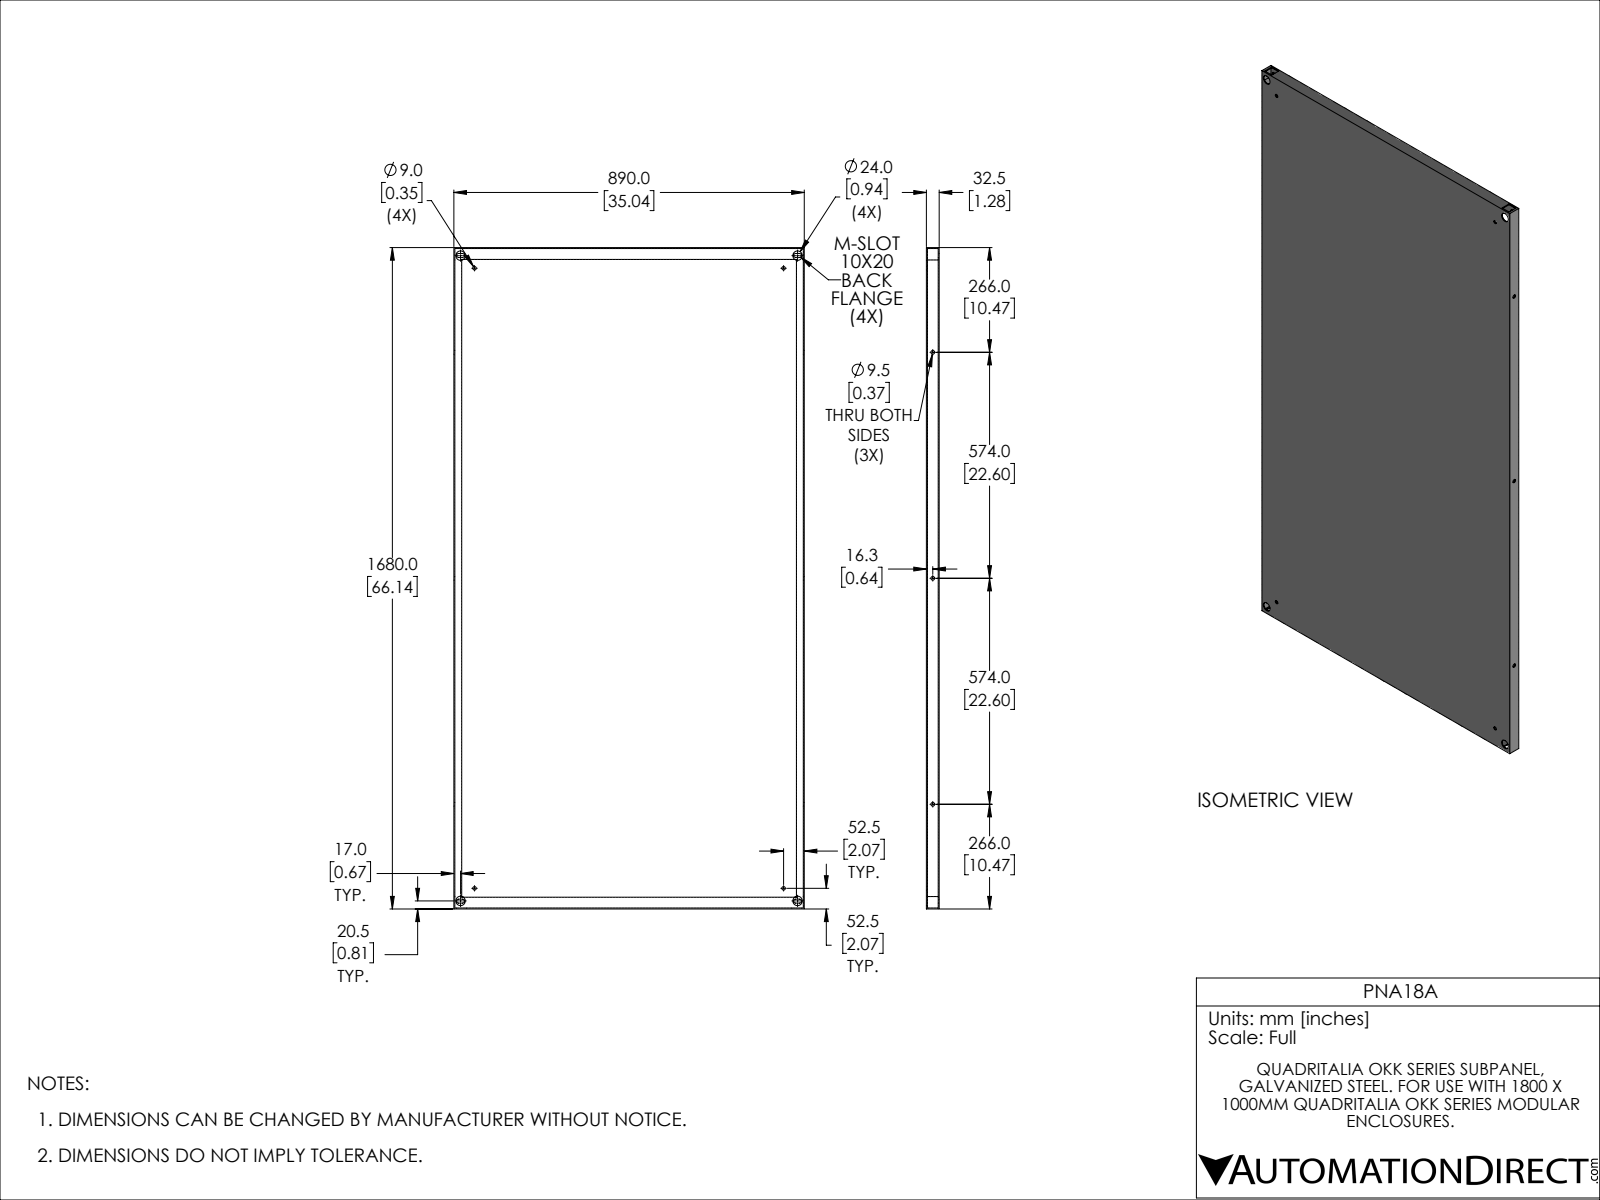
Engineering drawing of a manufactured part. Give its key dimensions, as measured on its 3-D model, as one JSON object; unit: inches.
{"part_name": "PNA18A", "step_written_by": "SolidWorks 2021 (CONFIG_CONTROL_DESIGN)", "units": "inches", "bodies": {"solids": 1, "faces": 70, "planar": 48, "cylindrical": 22, "other": 0}, "overall_size": [66.142, 35.039, 1.28], "volume_in3": 266.8, "surface_area_in2": 5445, "round_holes": [[0.354, 4], [0.945, 4], [0.374, 3]], "partial_cylinders_radius": [[0.197, 8]], "face_to_face_distances": [0.098, 1.181, 1.28, 1.083, 34.941, 35.039, 66.043, 34.843, 66.142, 65.945], "hole_center_spacings": [1.881, 32.328, 63.283, 71.037, 22.598, 30.906, 33.701, 62.008]}
